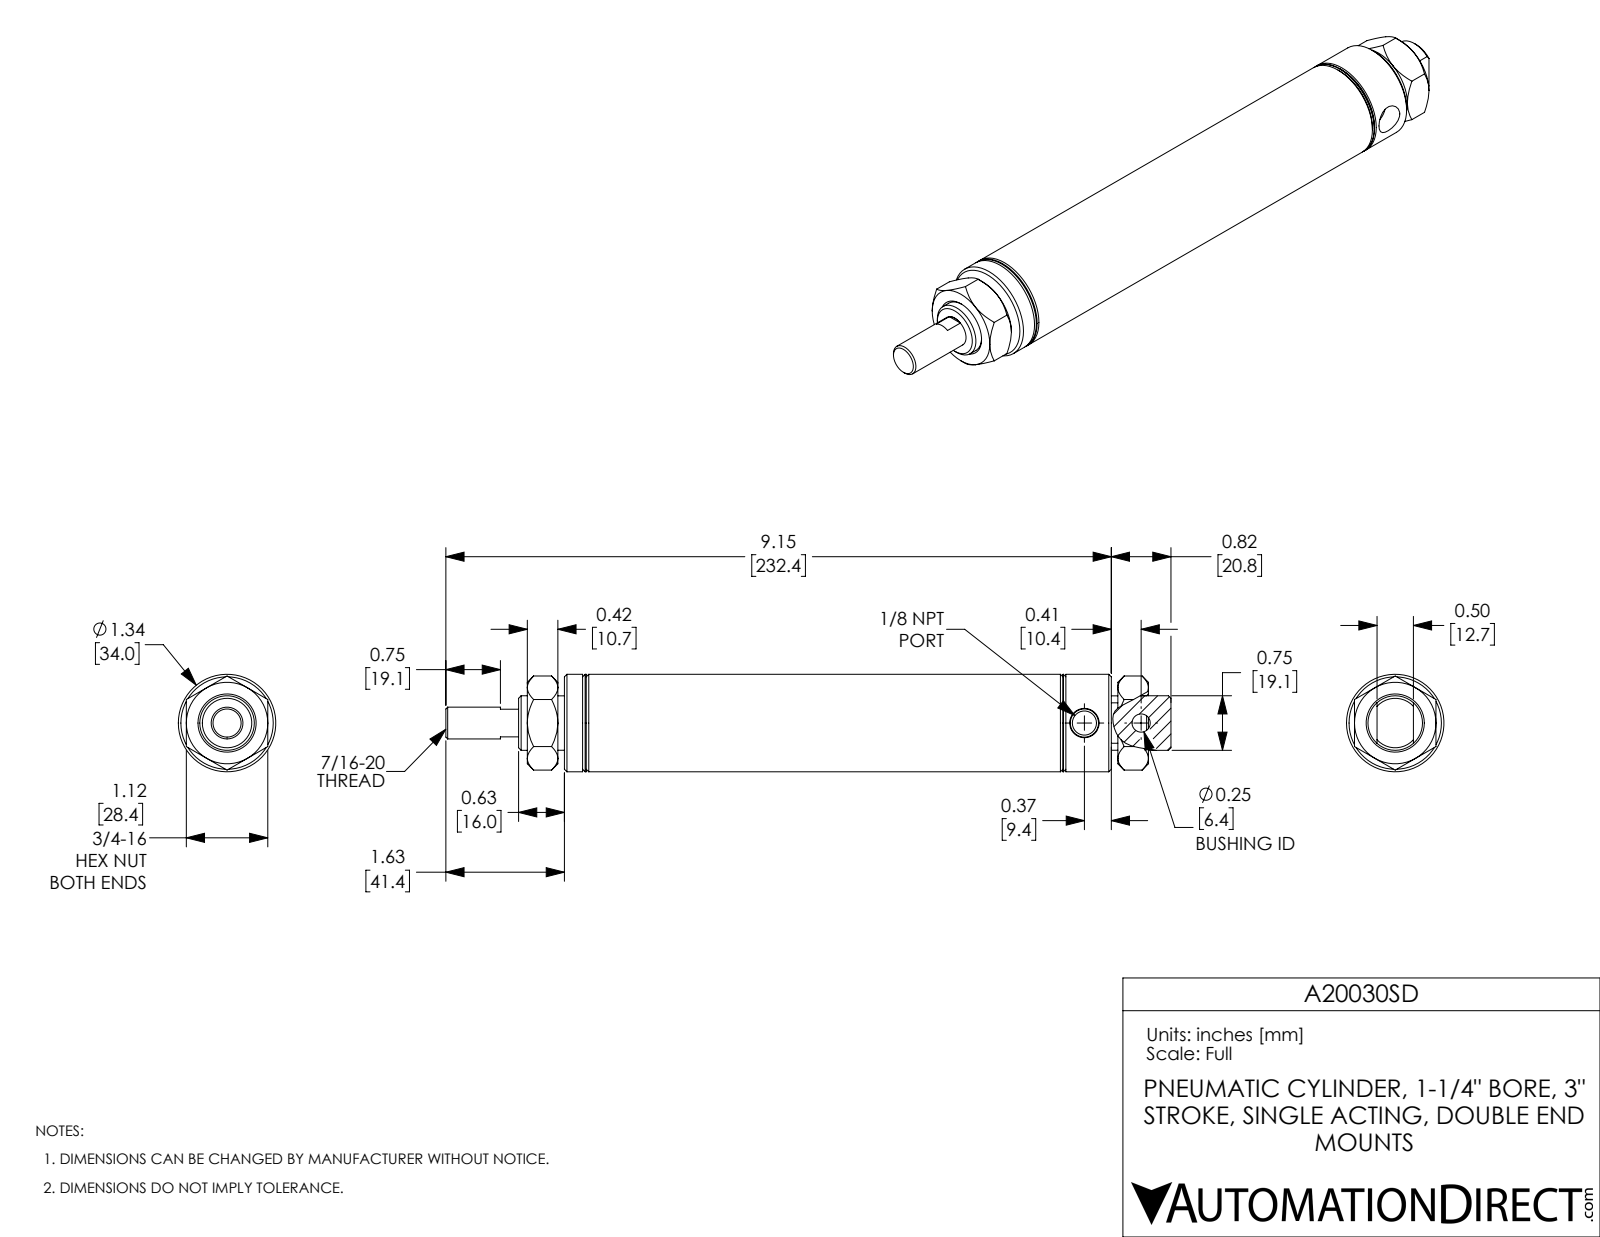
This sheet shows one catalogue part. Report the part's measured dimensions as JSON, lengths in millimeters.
{"part_name": "A20030SD_Mounting Nut_D-3556; A20030SD-Rod; A20030SD-MainBody; A20030SD", "step_written_by": "SolidWorks 2017 (AUTOMOTIVE_DESIGN)", "units": "millimeters", "bodies": {"solids": 4, "faces": 129, "planar": 41, "cylindrical": 34, "other": 54}, "overall_size": [253.2, 34, 34], "volume_mm3": 139600, "surface_area_mm2": 51340, "round_holes": [[6.4, 1], [8.4, 1], [11.1, 1], [19.1, 1], [31.8, 1]], "round_bosses_or_shafts": [[34, 1], [19, 1]], "face_to_face_distances": [12.7, 28.4, 88.9, 76.2, 53.3, 142.2, 13, 204, 20.6, 51.1], "hole_center_spacings": [19.8]}
